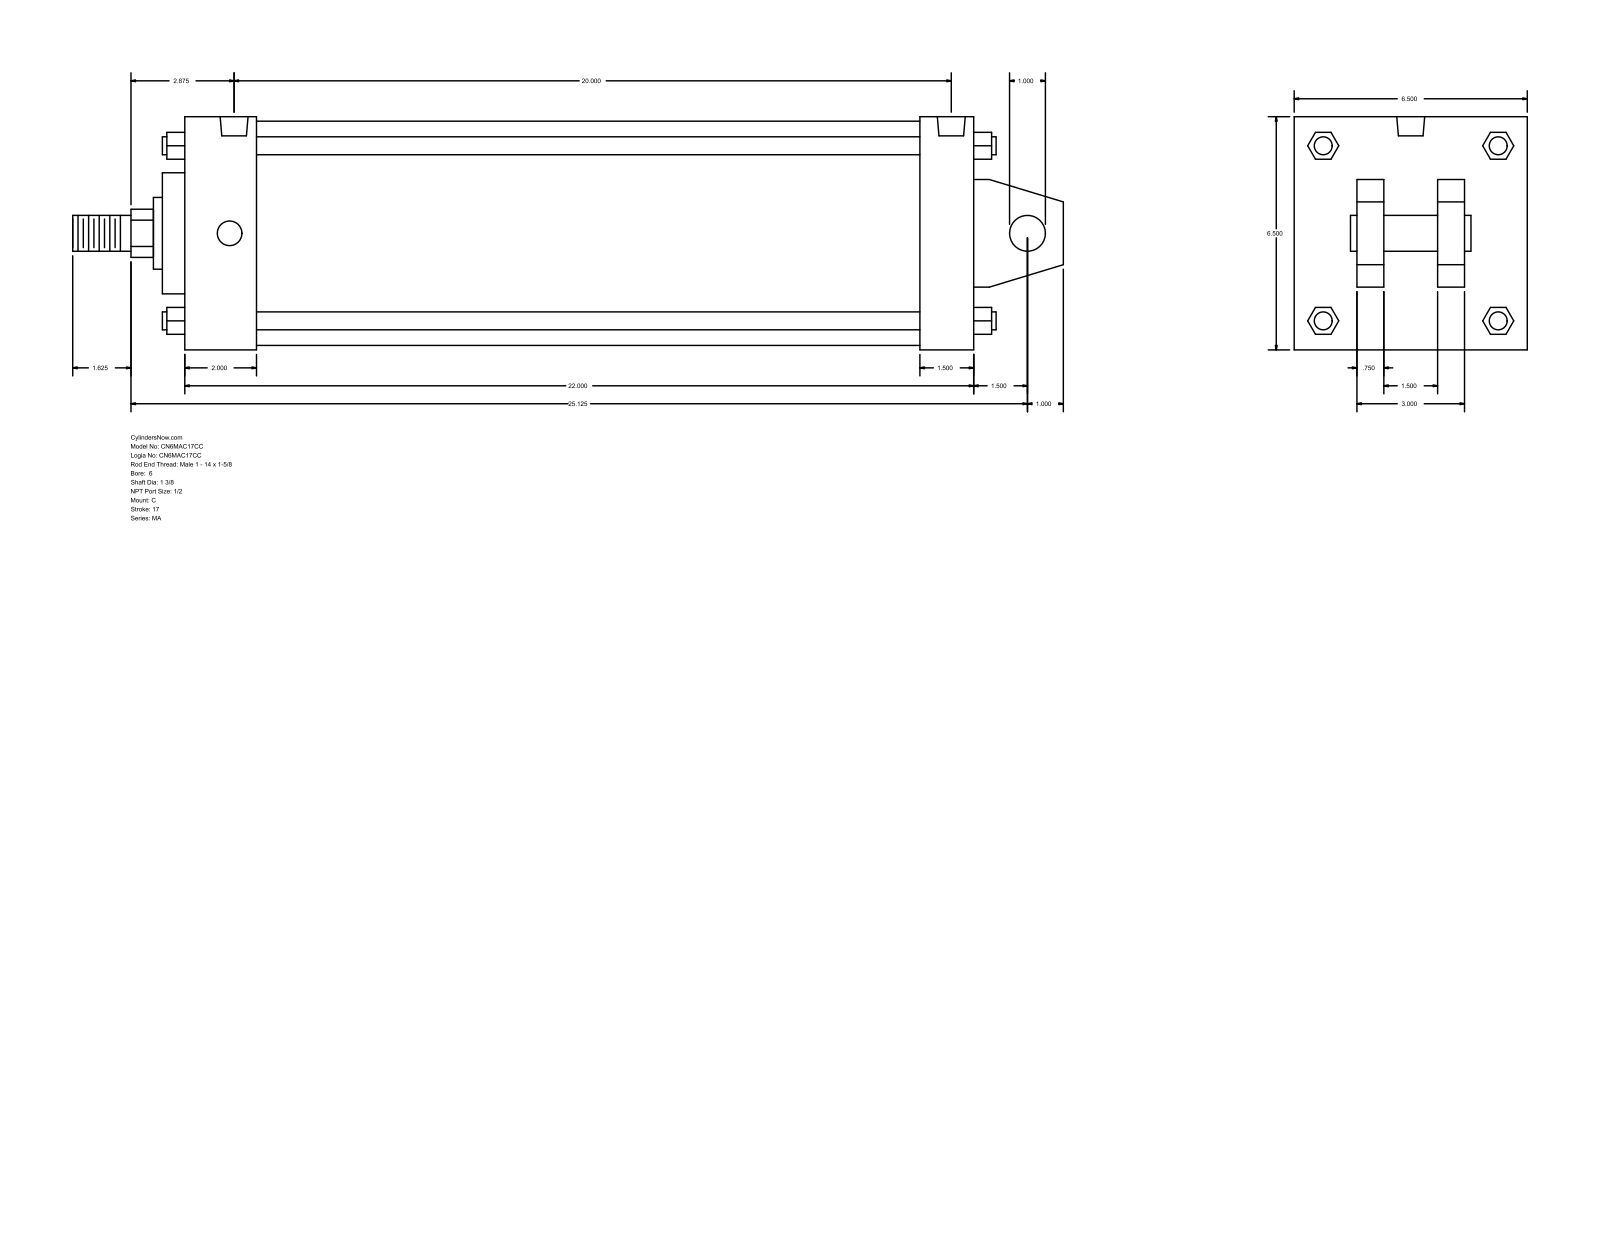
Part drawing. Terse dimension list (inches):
name: MA_C__0600_1.375
written by: GSSL Pune (CONFIG_CONTROL_DESIGN)
unit: in
bodies: 0 solids, 141 faces (109 planar, 32 cylindrical, 0 other)
size: 27.625 × 6.5 × 6.5
holes: 4× ⌀0.687, 2× ⌀0.778
bosses: 4× ⌀0.5, 2× ⌀1, 1× ⌀6.25, 1× ⌀3.375, 1× ⌀2, 1× ⌀1.375
rounds: 1× R0.672
face distances: 6.5, 22, 1.5, 0.75, 2.5, 4, 2, 1.75, 4.75, 20.5
hole spacings: 20, 0.125, 0.125, 19.875, 20, 20.125
